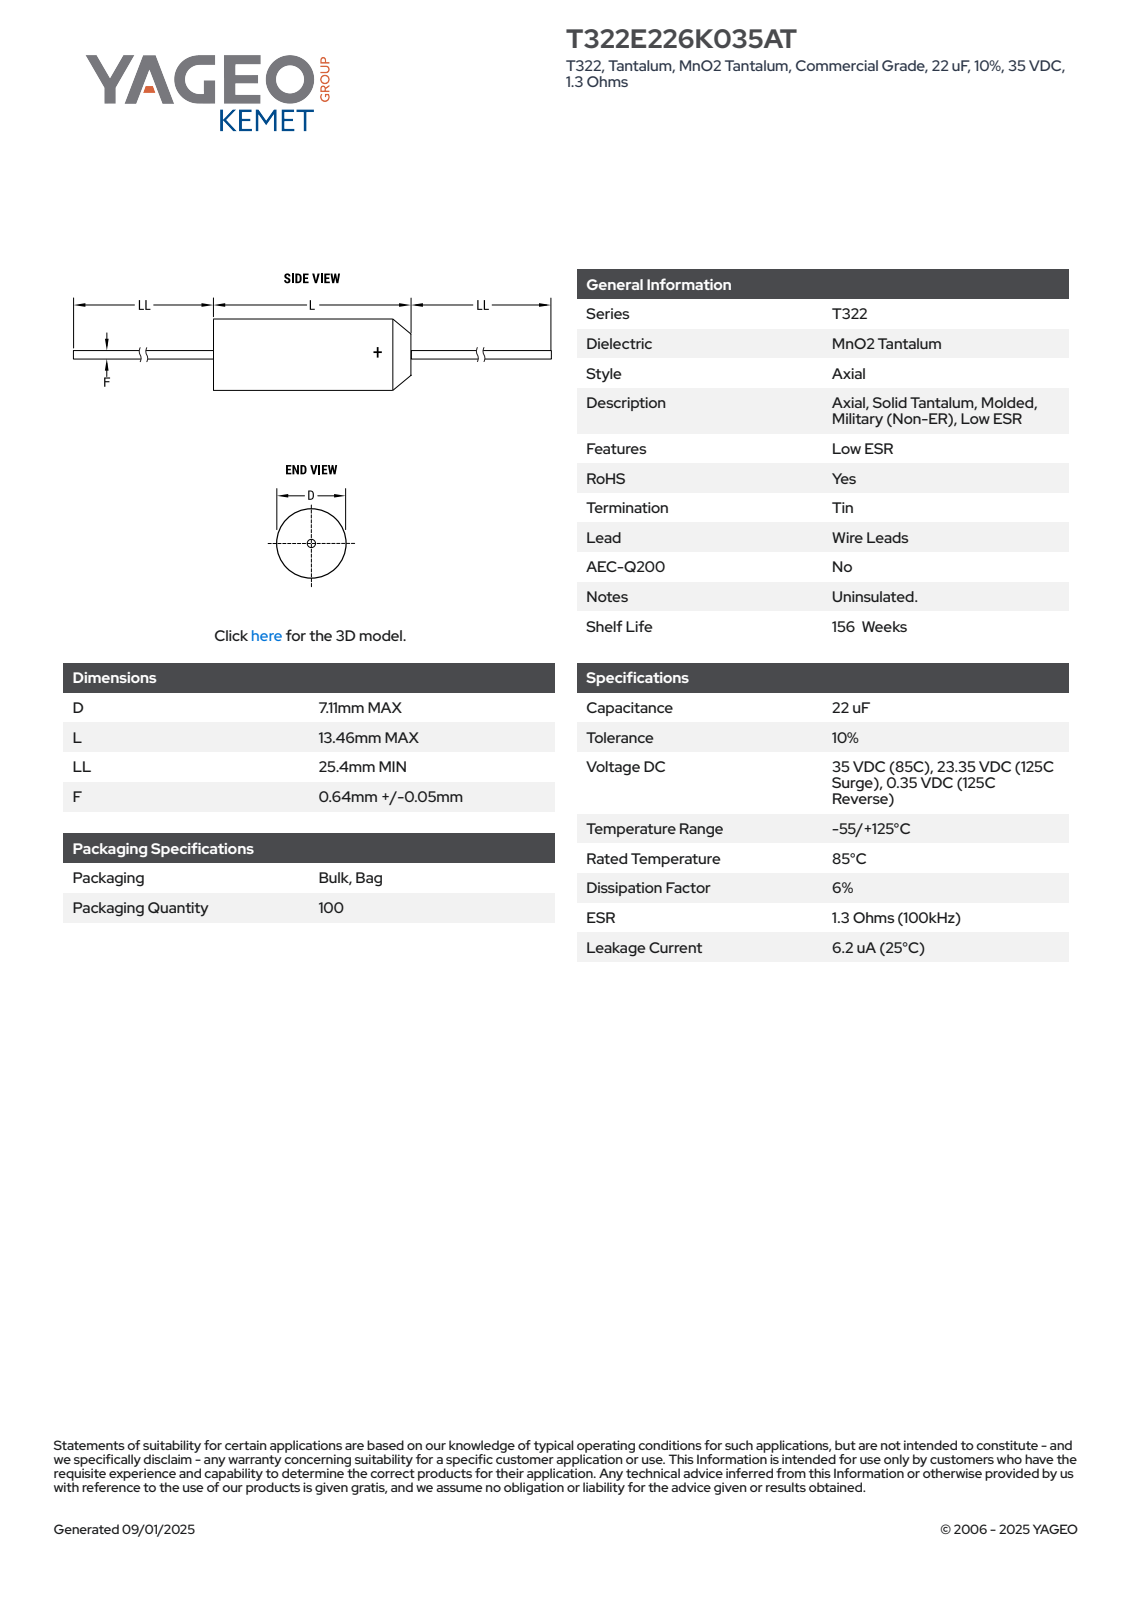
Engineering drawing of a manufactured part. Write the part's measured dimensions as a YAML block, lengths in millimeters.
part_name: "CTAM_D7.11L13.46LL25.4F0.69"
step_written_by: "SolidWorks 2020 (AUTOMOTIVE_DESIGN)"
units: millimeters
bodies: {solids: 1, faces: 102, planar: 38, cylindrical: 25, other: 39}
overall_size: [64.26, 7.11, 7.11]
volume: 548
surface_area: 480
round_bosses_or_shafts:
  - {diameter: 7.11, count: 1}
  - {diameter: 0.69, count: 1}
partial_cylinders:
  - {radius: 3.54, count: 1}
face_to_face_distances: [13.46, 25.4, 38.86, 64.26, 37.16, 11.76, 1.7, 27.1, 37.26, 11.86]
